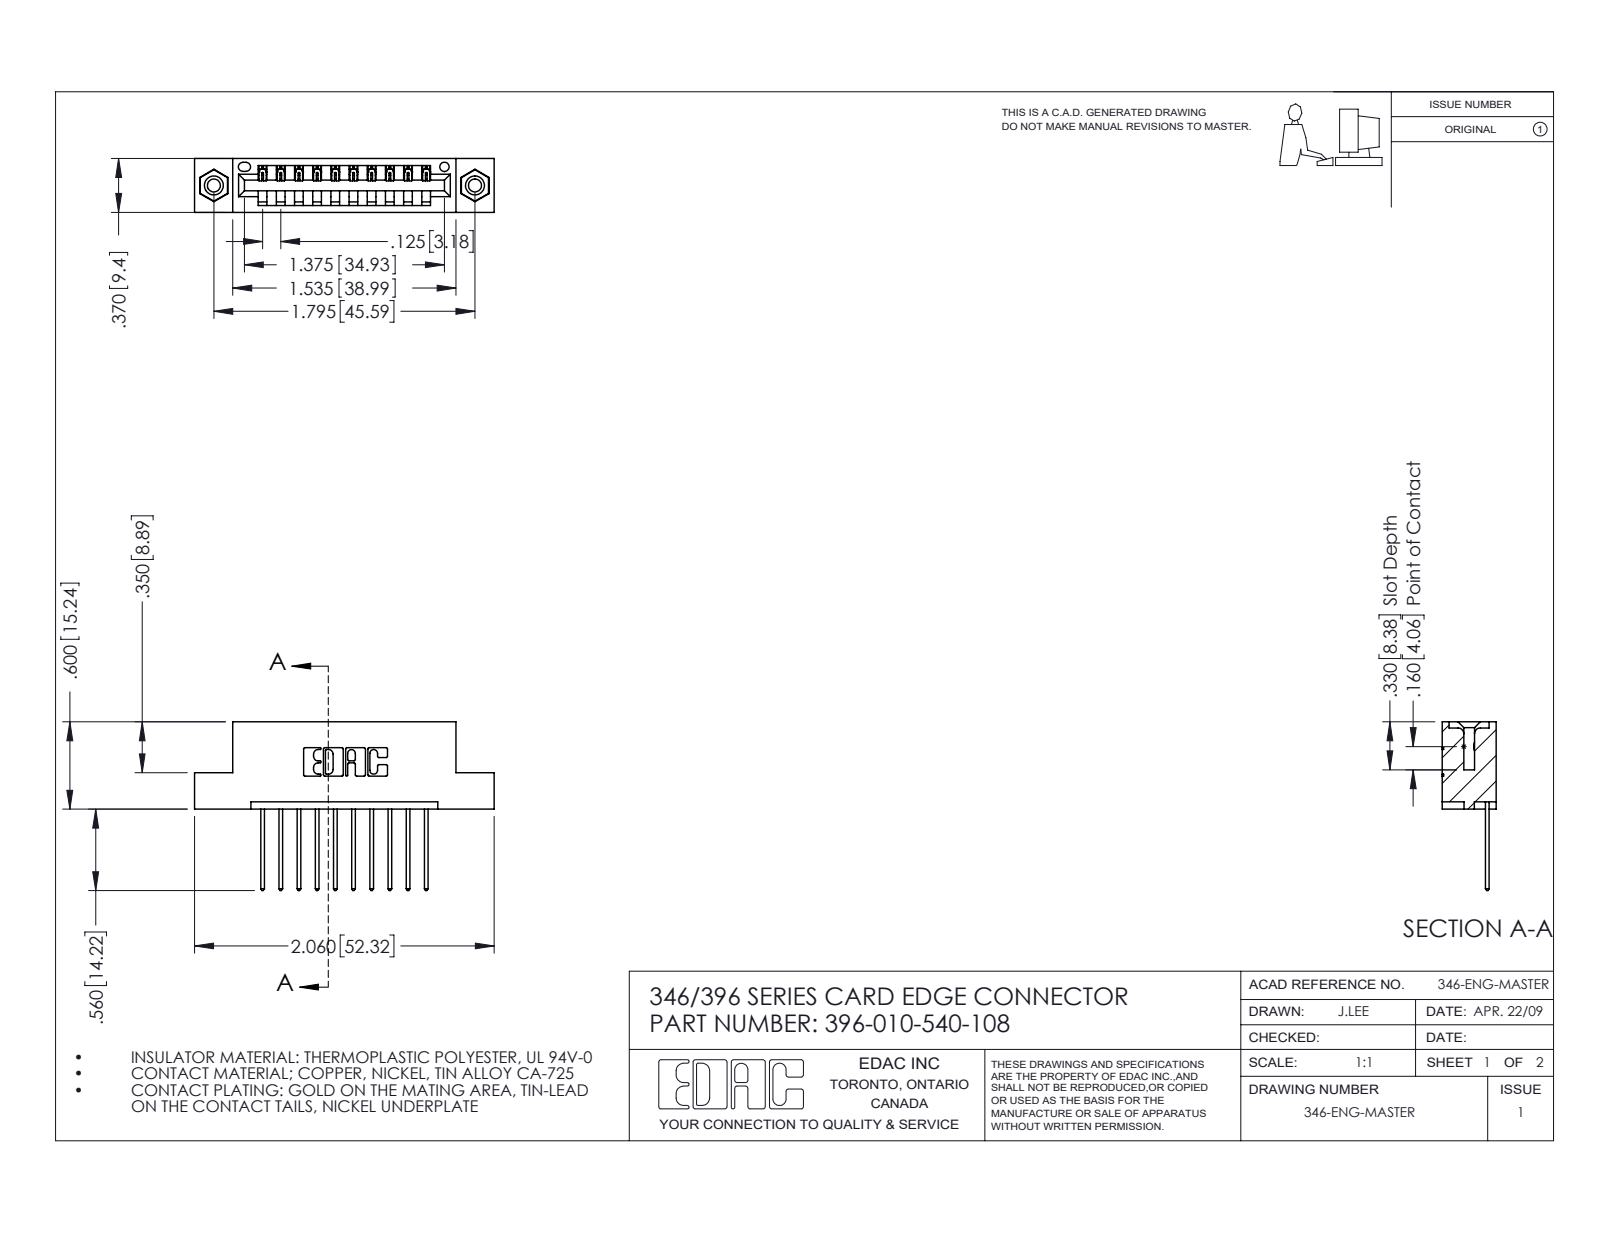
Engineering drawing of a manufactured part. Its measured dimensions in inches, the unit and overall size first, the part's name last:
Units: inches
Overall size (bounding box): 2.06 × 1.16 × 0.37
Round holes (diameter × count): ⌀0.089 ×2, ⌀0.125 ×2, ⌀0.156 ×2, ⌀0.064 ×1
Round bosses / shafts (diameter × count): ⌀0.155 ×2
Partial cylindrical surfaces — rounded edges, fillets, slot ends (radius × count): R0.01 ×22, R0.006 ×20, R0.01 ×20, R0.007 ×6, R0.031 ×6, R0.026 ×3, R0.031 ×2, R0.04 ×2
Main face-to-face distances: 0.25, 0.048, 0.322, 0.37, 0.072, 0.298, 0.025, 0.148, 0.222, 0.1
Hole centre spacings: 0.246, 1.59, 1.795
Volume: 0.293 in³ · Surface area: 8.941 in²
Bodies: 13 solids, 762 faces (508 planar, 238 cylindrical, 16 other)
Part name (STEP PRODUCT): 346 Part_Flush Mounting Lugs - 0.156 Dia-TI; 345-292-001_345-293-140; 396-010-540-108; 345-250-001_345-250-003-102
STEP written by: SolidWorks 2016 (CONFIG_CONTROL_DESIGN)
